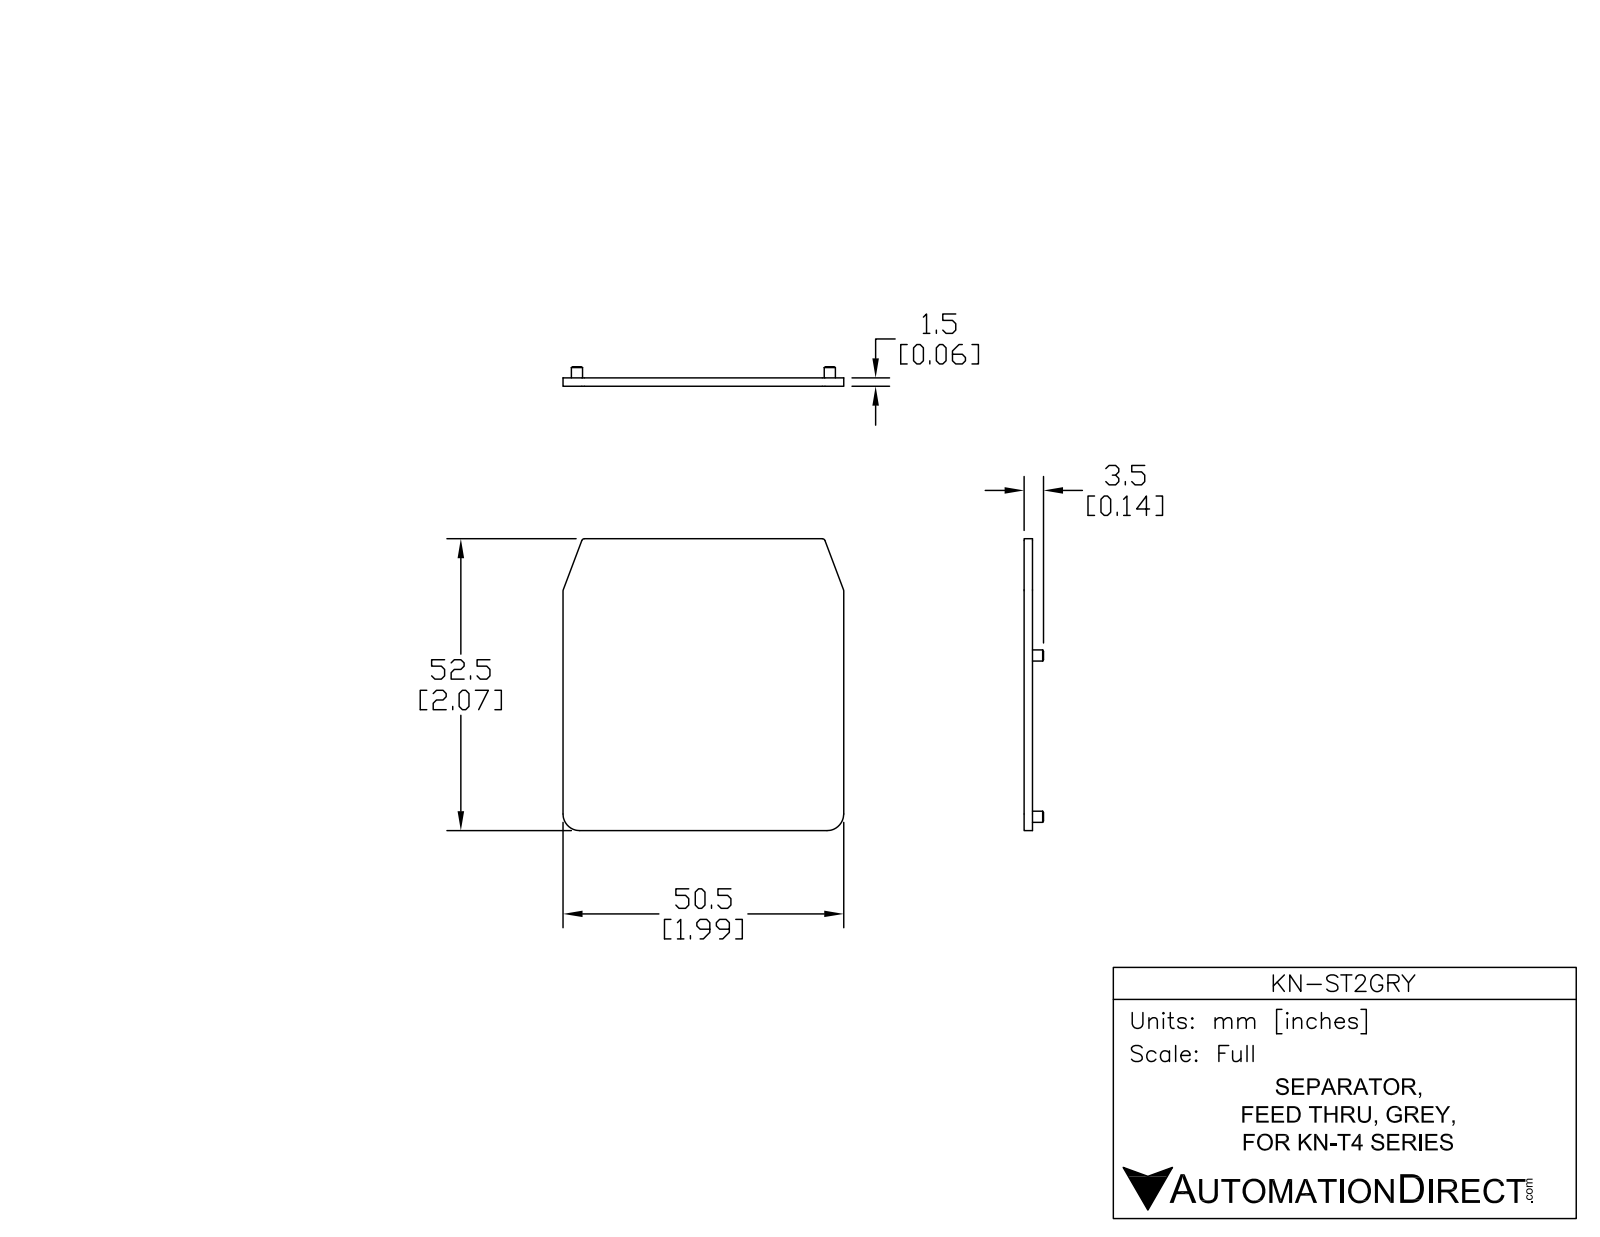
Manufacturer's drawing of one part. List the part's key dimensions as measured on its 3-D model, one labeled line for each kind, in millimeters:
Part name (STEP PRODUCT): KN-ST2
STEP written by: SolidWorks 2014 (AUTOMOTIVE_DESIGN)
Units: millimetres
Bodies: 1 solid, 46 faces (16 planar, 22 cylindrical, 8 other)
Overall size (bounding box): 52.5 × 50.5 × 3.5
Volume: 3 941 mm³ · Surface area: 5 599 mm²
Round holes (diameter × count): ⌀1 ×4
Round bosses / shafts (diameter × count): ⌀2 ×4
Partial cylindrical surfaces — rounded edges, fillets, slot ends (radius × count): R0.5 ×4, R3 ×2
Main face-to-face distances: 1.5, 52.5, 50.5, 2, 3.5
Hole centre spacings: 29, 45.5, 53.96
